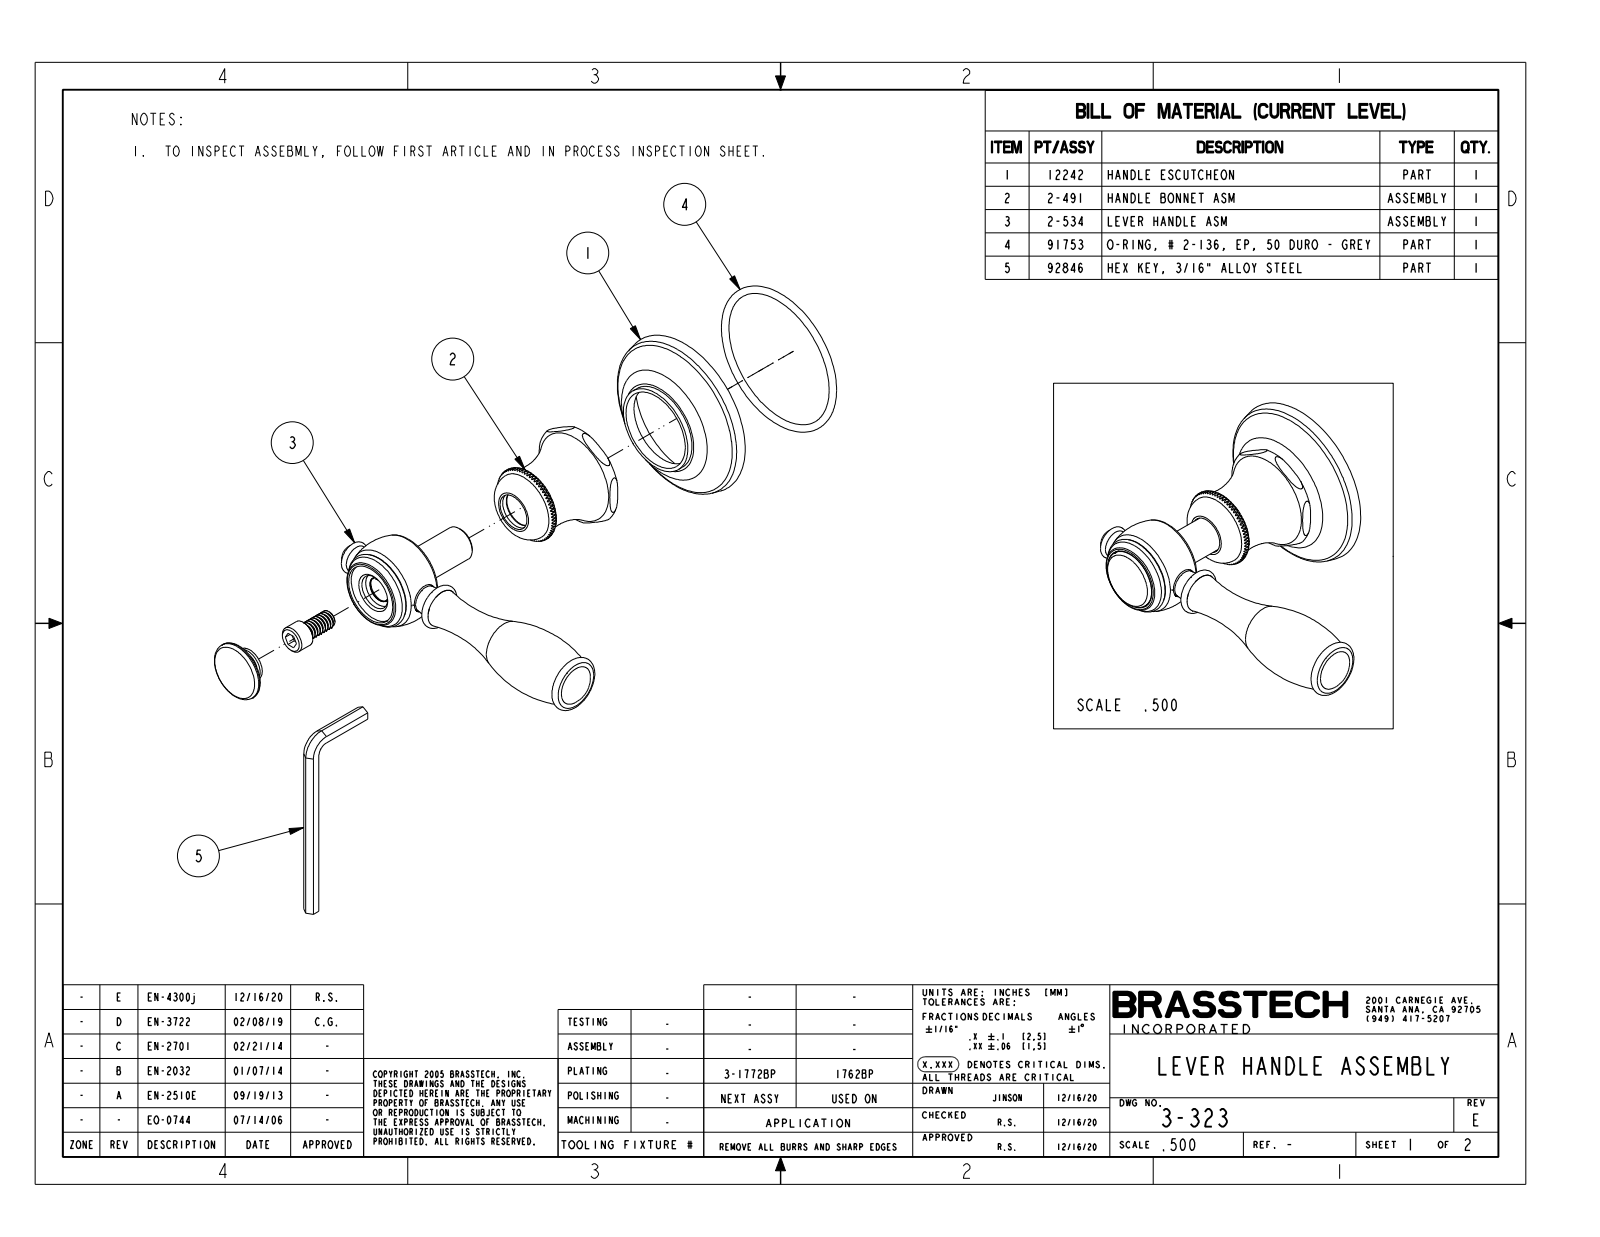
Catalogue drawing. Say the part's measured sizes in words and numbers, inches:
The part is named "30349". Its 3-D file was written by "CREO PARAMETRIC BY PTC INC, 2018400 (CONFIG_CONTROL_DESIGN)". It is 1 solid with 225 faces: 155 planar, 14 cylindrical and 56 other. Overall it measures 4.829 by 3.41 by 2.365 inches. Its volume is 4.797 cubic inches and its surface area 27.66 square inches. Round holes: 1 of diameter 0.41, 1 of diameter 0.855. Round bosses or shafts: 1 of diameter 0.84, 1 of diameter 0.5, 1 of diameter 0.392. The main face-to-face distances are 2.54, 1.375, 3.25, 0.71, 0.75, 3.3, 0.76, 0.05, 4.212, 2.837.
